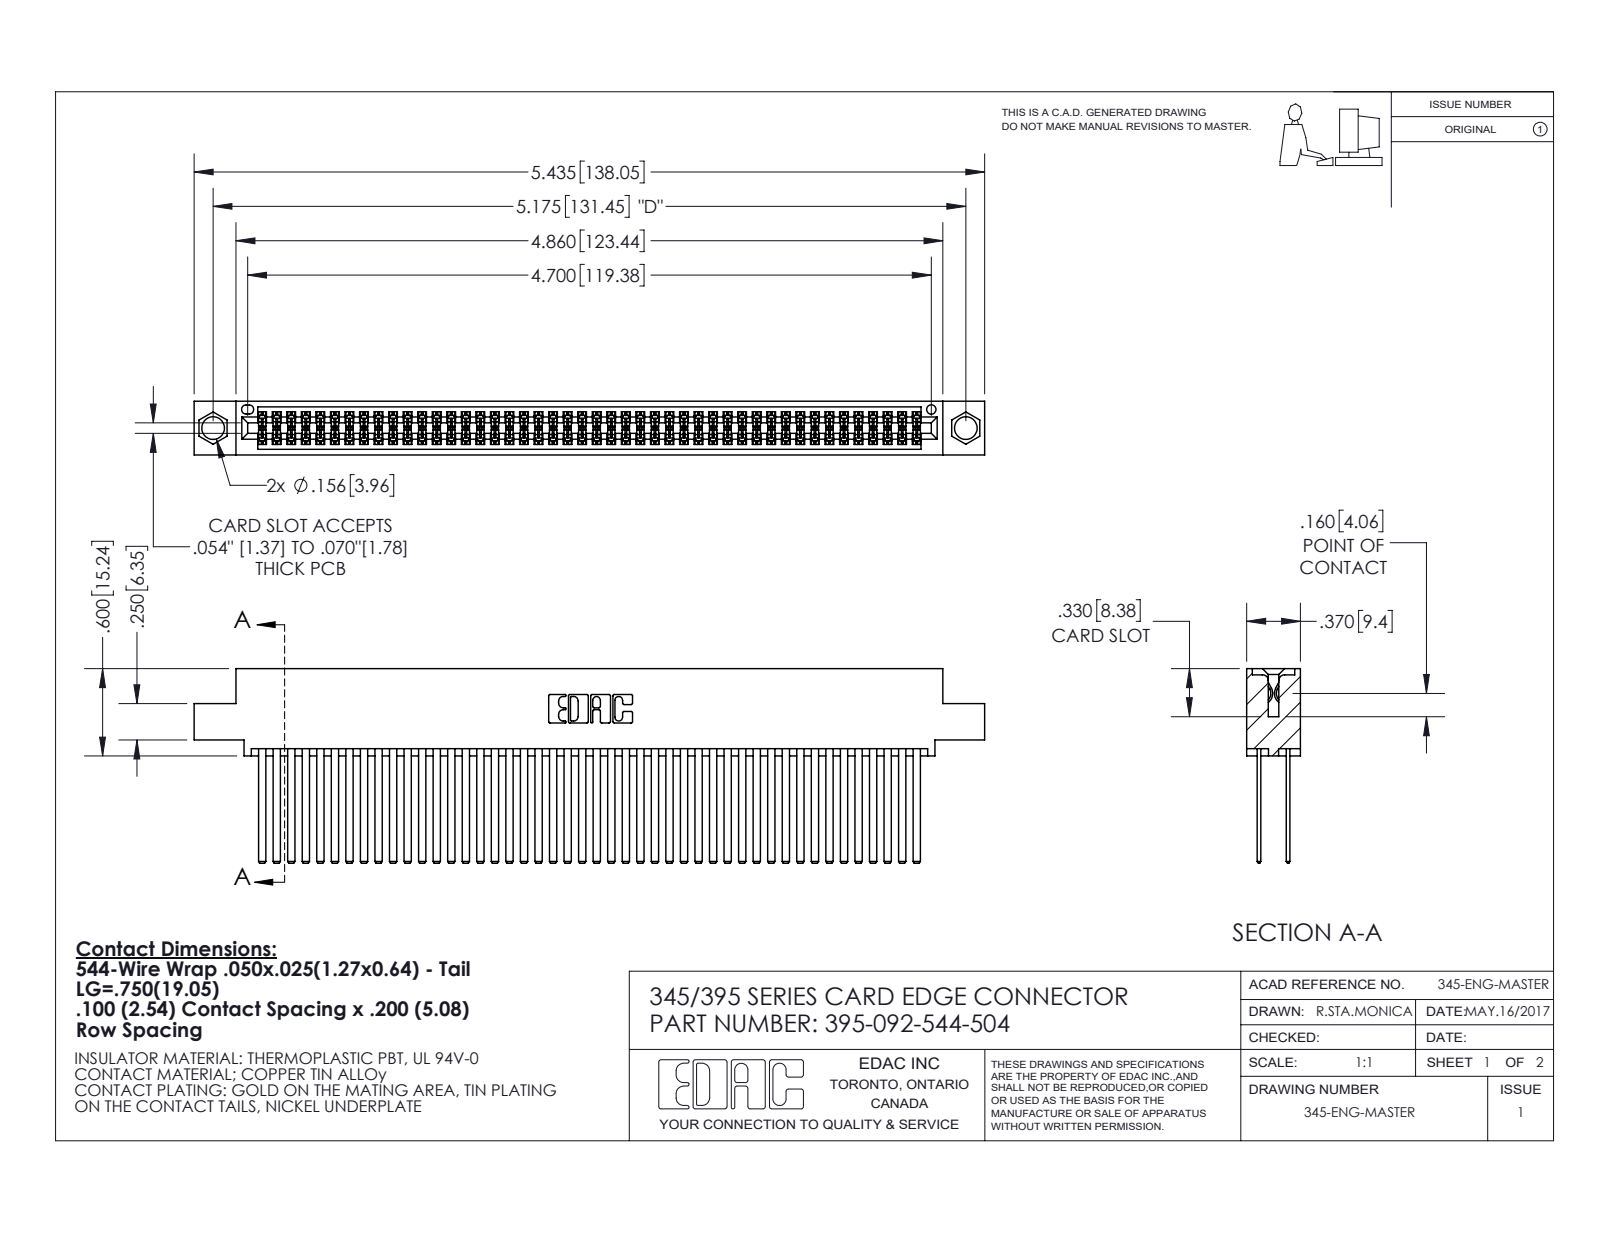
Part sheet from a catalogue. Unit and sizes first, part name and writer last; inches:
Units: inches
Overall size (bounding box): 5.435 × 1.337 × 0.37
Round holes (diameter × count): ⌀0.156 ×2, ⌀0.064 ×1
Partial cylindrical surfaces — rounded edges, fillets, slot ends (radius × count): R0.006 ×138, R0.01 ×22, R0.007 ×6, R0.031 ×6, R0.026 ×3, R0.014 ×2, R0.019 ×2, R0.022 ×2
Main face-to-face distances: 0.2, 0.025, 0.298, 0.072, 0.098, 0.272, 0.225, 0.175, 0.37, 0.05
Hole centre spacings: 0.27, 4.939, 5.175
Volume: 0.888 in³ · Surface area: 39.25 in²
Bodies: 93 solids, 4192 faces (2766 planar, 1426 cylindrical, 0 other)
Part name (STEP PRODUCT): 345 Part_0.110 Offset - 0.156 Dia-TI; 395-092-544-504; 345-292-001_345-293-144
STEP written by: SolidWorks 2020 (CONFIG_CONTROL_DESIGN)
